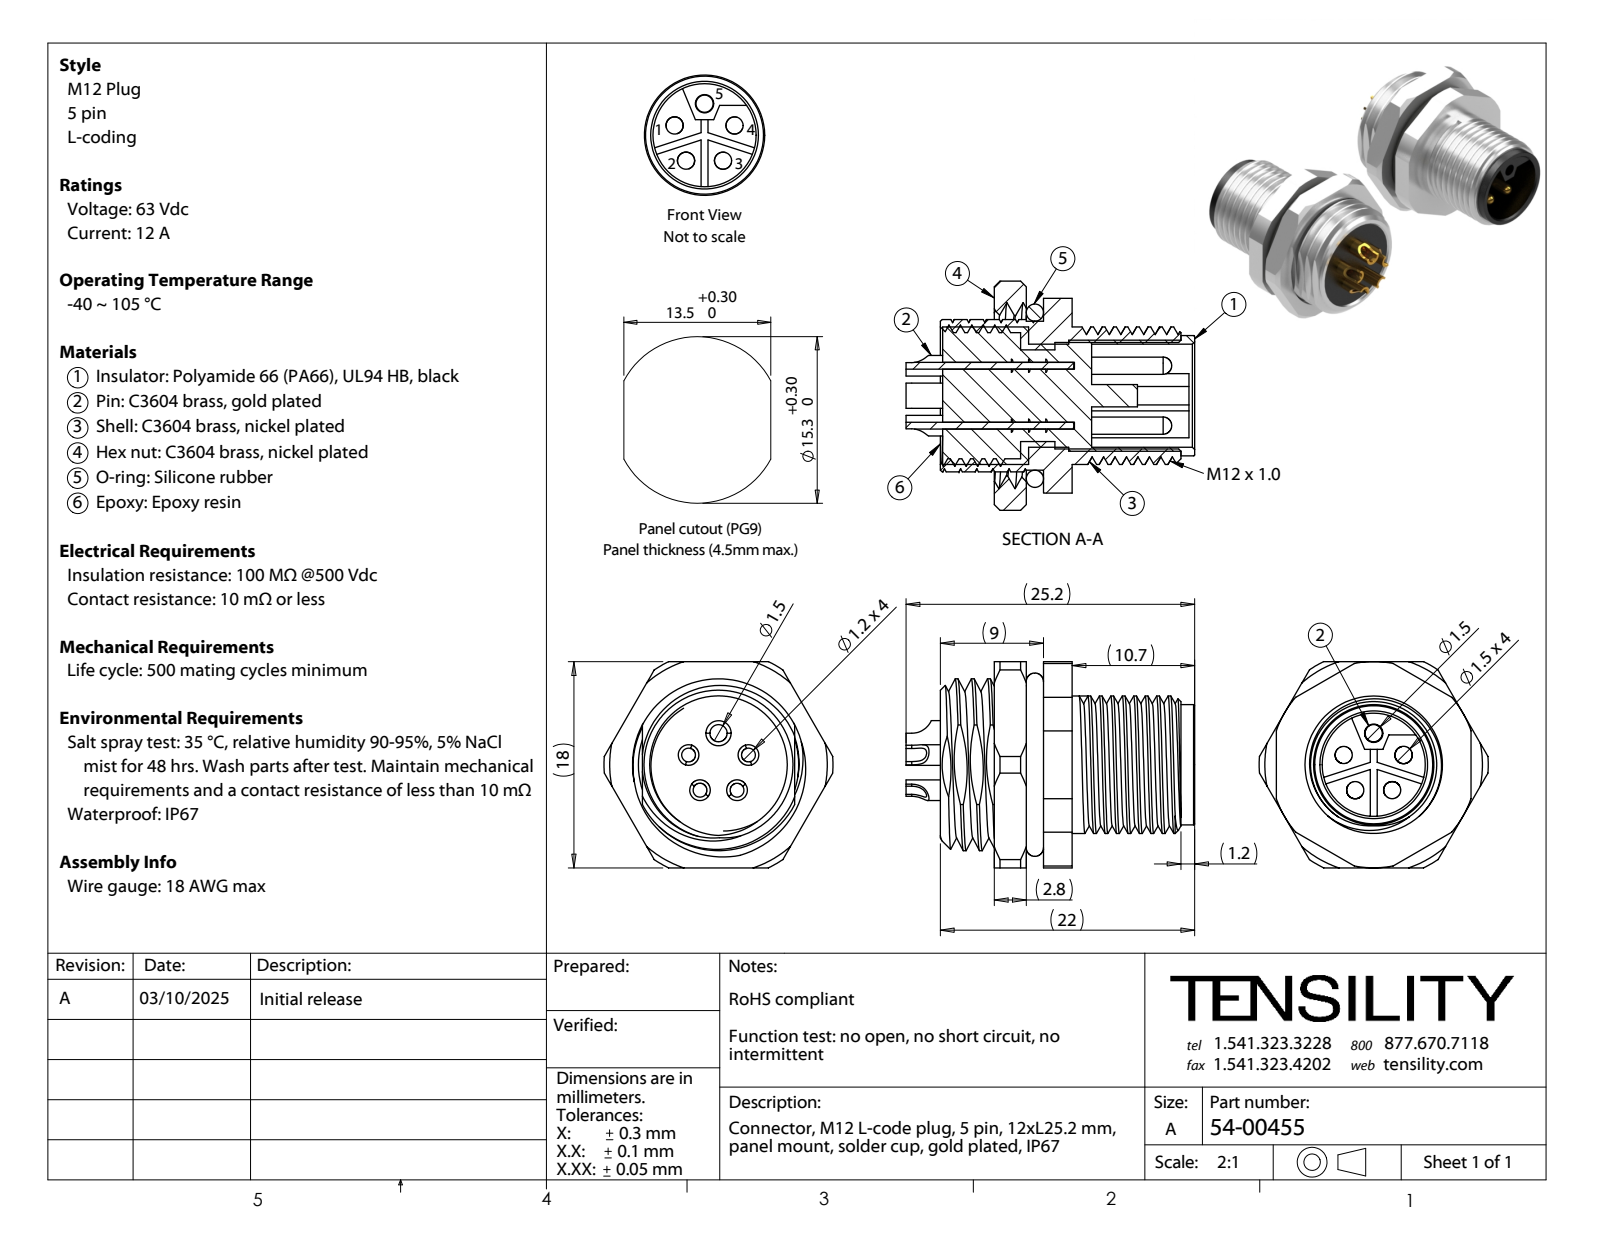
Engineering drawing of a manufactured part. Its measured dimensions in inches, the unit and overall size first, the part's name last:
Units: inches
Overall size (bounding box): 0.992 × 0.787 × 0.709
Round holes (diameter × count): ⌀0.059 ×5, ⌀0.047 ×4, ⌀0.063 ×1, ⌀0.315 ×1, ⌀0.354 ×1, ⌀0.366 ×1, ⌀0.433 ×1, ⌀0.551 ×1
Round bosses / shafts (diameter × count): ⌀0.071 ×4, ⌀0.512 ×1, ⌀0.472 ×1, ⌀0.413 ×1, ⌀0.382 ×1, ⌀0.087 ×1
Partial cylindrical surfaces — rounded edges, fillets, slot ends (radius × count): R0.067 ×4, R0.073 ×1, R0.295 ×1, R0.354 ×1, R0.394 ×1
Main face-to-face distances: 0.177, 0.059, 0.268, 0.346, 0.098, 0.157, 0.287, 0.445, 0.11, 0.169
Hole centre spacings: 0.108, 0.206, 0.128, 0.127, 0.206
Volume: 0.193 in³ · Surface area: 9.164 in²
Bodies: 9 solids, 368 faces (106 planar, 158 cylindrical, 104 other)
Part name (STEP PRODUCT): 54-00455; 54-00455-02; 54-00455-03; 54-00455-04 (+3 more)
STEP written by: SolidWorks 2021 (CONFIG_CONTROL_DESIGN)
